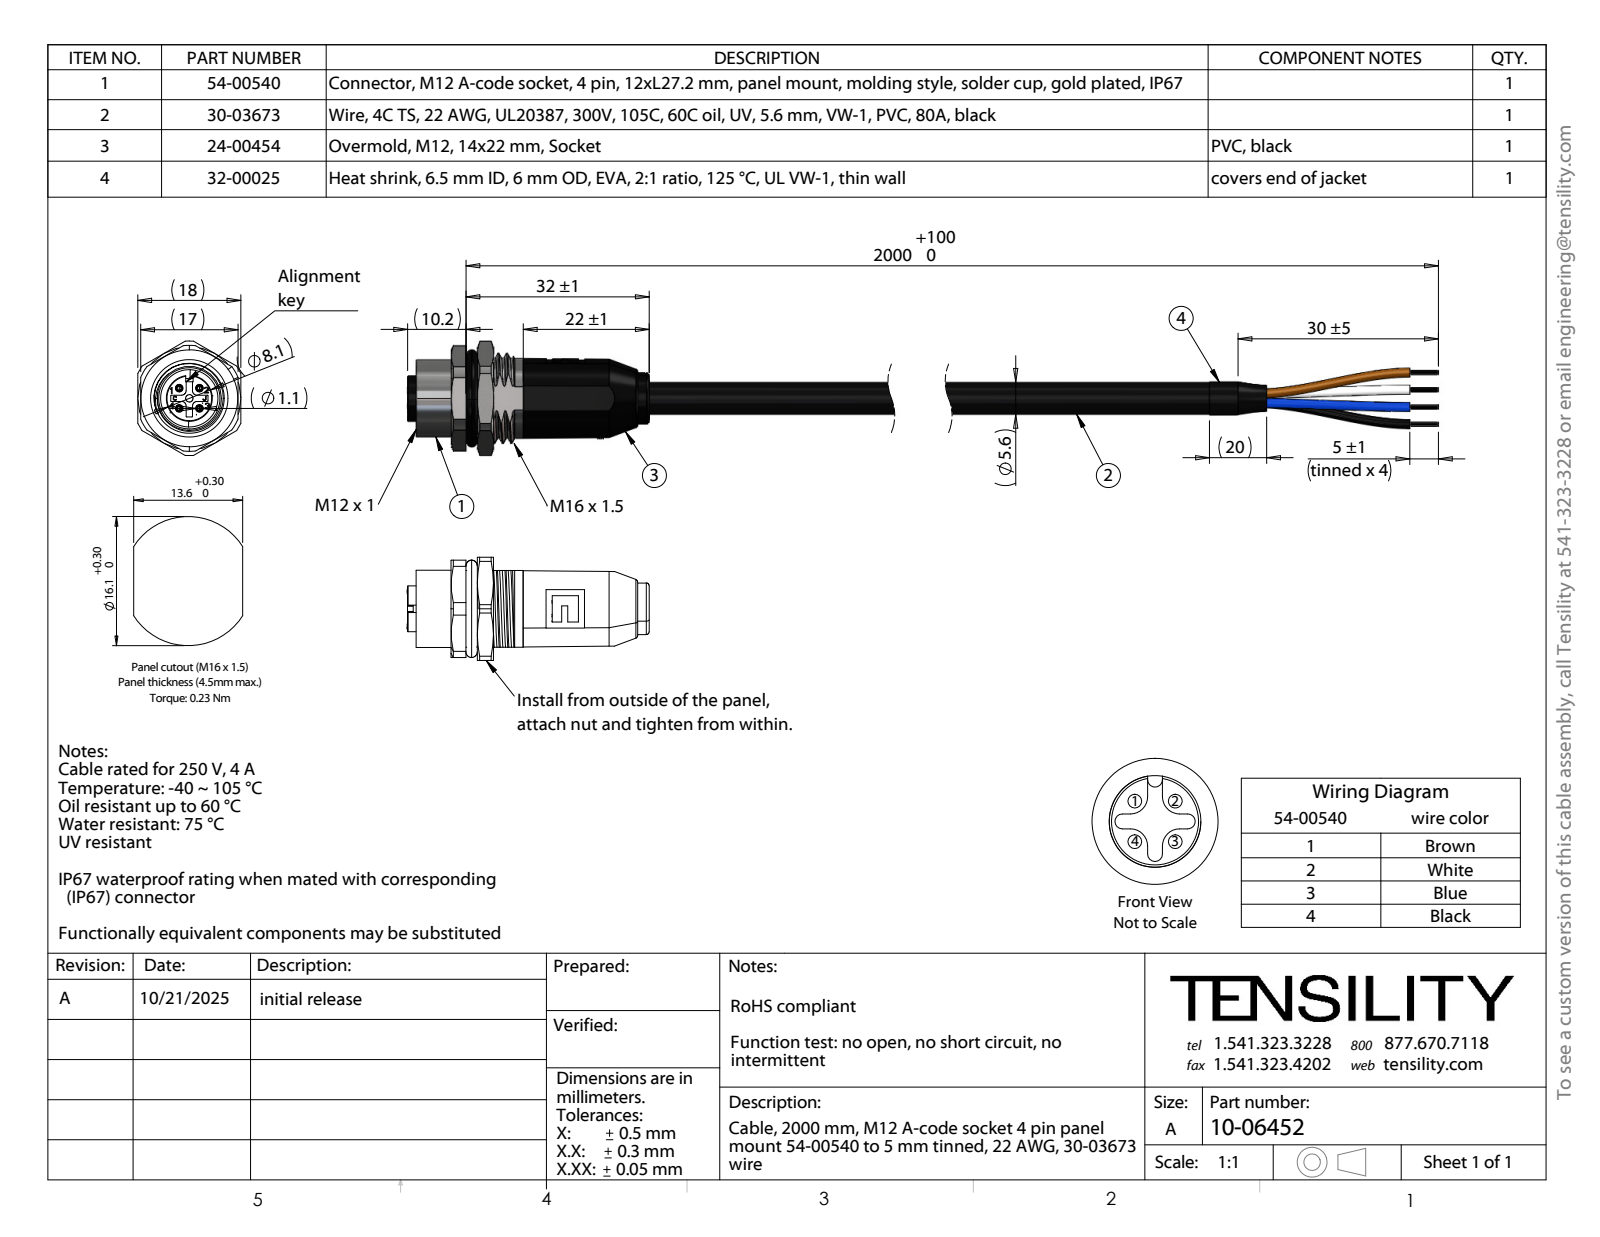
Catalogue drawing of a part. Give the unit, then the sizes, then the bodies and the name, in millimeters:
Units: millimetres
Overall size (bounding box): 227.24 × 20 × 18
Round holes (diameter × count): ⌀1.6 ×8, ⌀1.3 ×5, ⌀1.2 ×4, ⌀3.88 ×1, ⌀4.28 ×1, ⌀6.5 ×1, ⌀7.5 ×1, ⌀8.8 ×1, ⌀9.1 ×1, ⌀9.6 ×1, ⌀11.2 ×1, ⌀12.2 ×1
Round bosses / shafts (diameter × count): ⌀1.7 ×4, ⌀1.56 ×4, ⌀1.52 ×4, ⌀13.95 ×1, ⌀13.5 ×1, ⌀12.5 ×1, ⌀11 ×1, ⌀10.7 ×1
Partial cylindrical surfaces — rounded edges, fillets, slot ends (radius × count): R0.1 ×6, R0.8 ×4, R0.5 ×3, R7.04 ×1, R7.9 ×1, R9.25 ×1, R10 ×1
Main face-to-face distances: 0.5, 10, 2, 9.5, 11.5, 18, 7.5, 2.6, 1.5, 5.1
Hole centre spacings: 0.48, 0.37, 1.62, 0.31, 0.33, 1.78, 0.32, 1.45
Volume: 9 951 mm³ · Surface area: 34 725 mm²
Bodies: 155 solids, 1614 faces (715 planar, 659 cylindrical, 240 other)
Part name (STEP PRODUCT): 24-00454; 54-00540; 56-00046; 32-00025_10 mm (+2 more)
STEP written by: SolidWorks 2025 (CONFIG_CONTROL_DESIGN)
